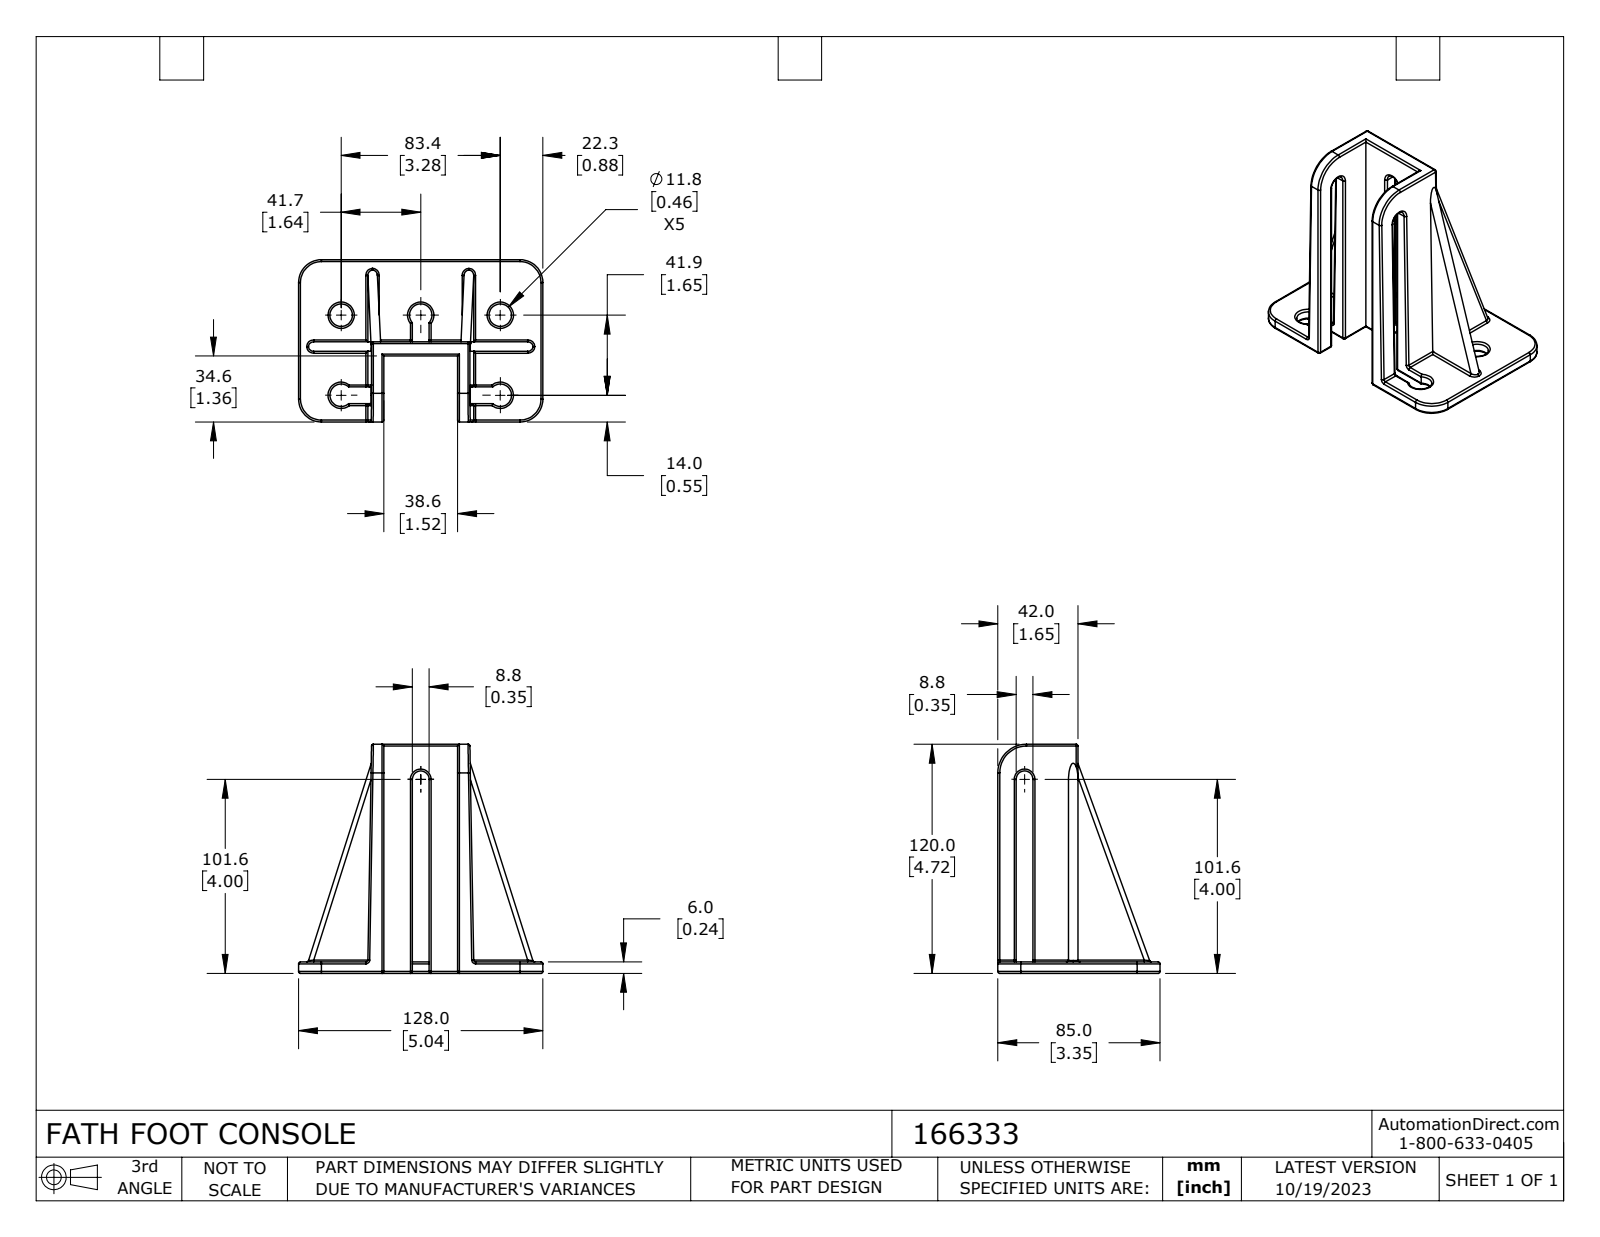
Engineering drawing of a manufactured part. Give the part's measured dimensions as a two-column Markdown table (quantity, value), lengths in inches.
| quantity | value |
| --- | --- |
| part name | 166333 |
| STEP written by | SolidWorks 2023 (CONFIG_CONTROL_DESIGN) |
| units | inches |
| bodies | 1 solid, 187 faces (28 planar, 91 cylindrical, 68 other) |
| overall size | 5.039 × 4.724 × 3.346 |
| volume | 10.28 in³ |
| surface area | 94.98 in² |
| round holes (diameter × count) | 0.465 × 2 |
| partial cylindrical surfaces (radius × count) | 0.039 × 49, 0.098 × 4, 0.472 × 4, 0.232 × 3, 0.173 × 2, 0.591 × 1 |
| main face-to-face distances | 0.236, 0.197, 0.293, 1.52, 0.096, 0.346, 1.36, 1.457, 1.654, 0.378 |
| hole center spacings | 3.282 |
